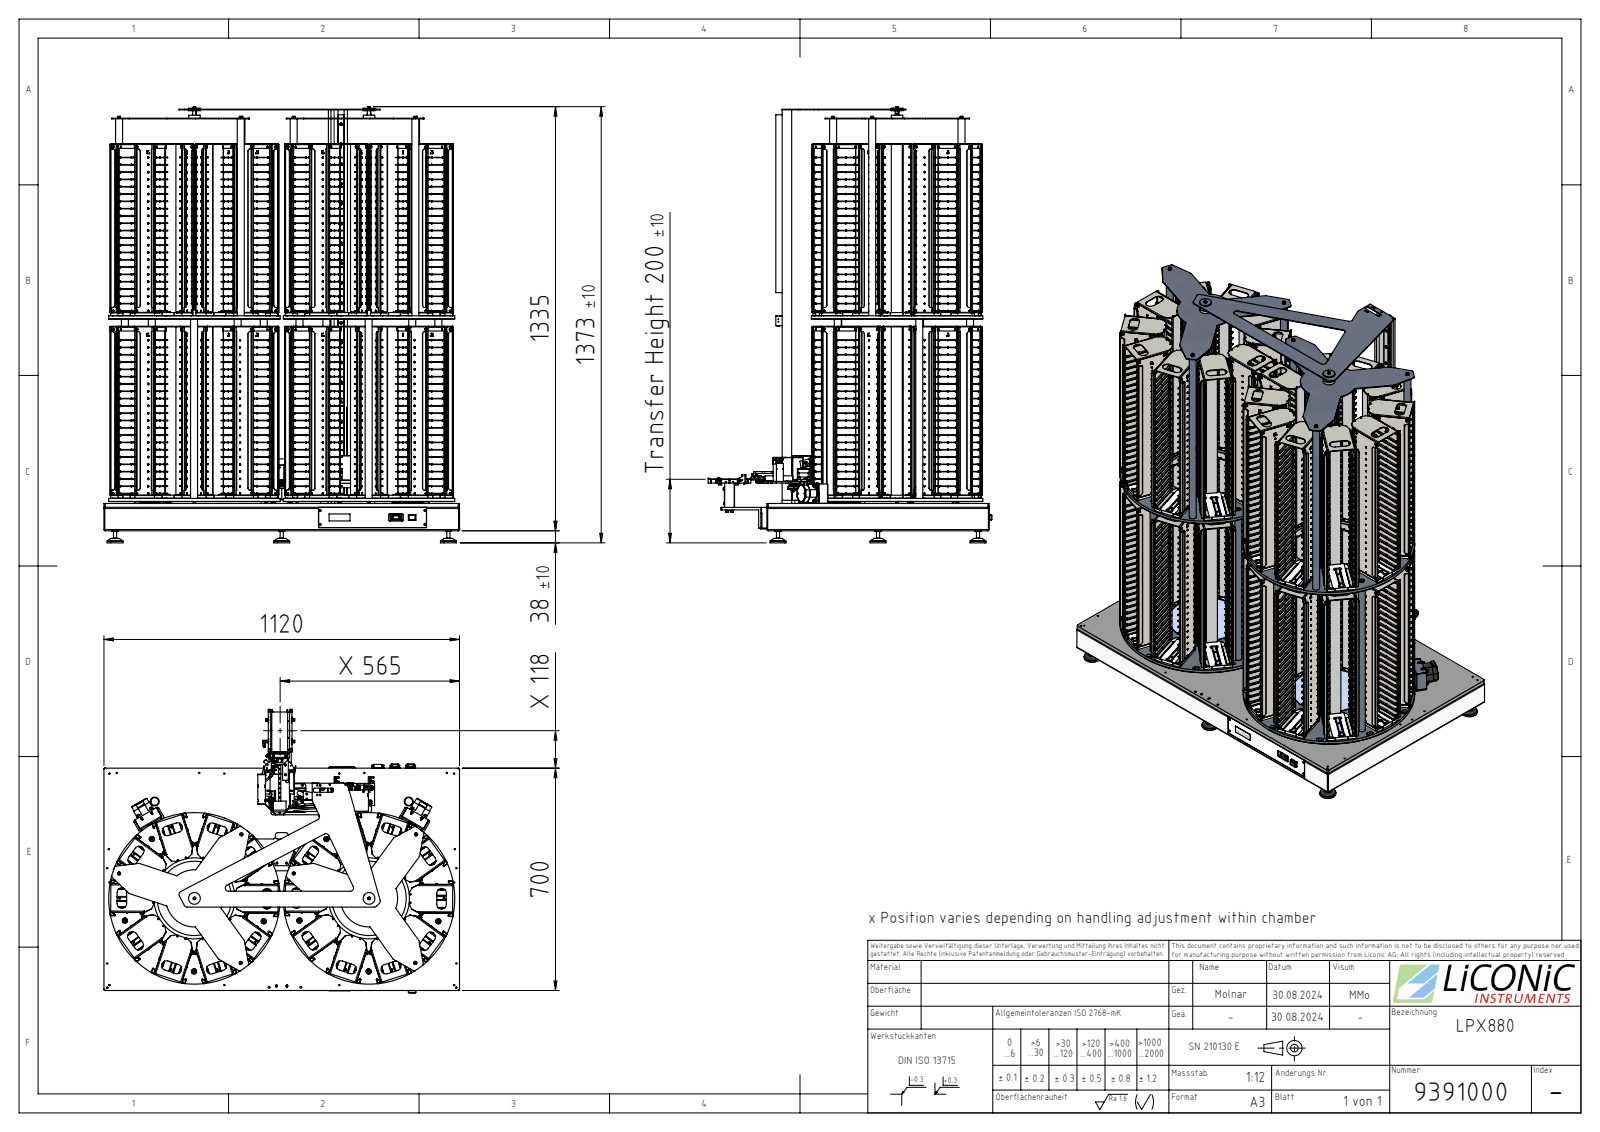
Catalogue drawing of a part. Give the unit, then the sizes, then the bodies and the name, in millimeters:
Units: millimetres
Overall size (bounding box): 1365.3 × 1120 × 893.98
Round holes (diameter × count): ⌀4 ×176, ⌀2.5 ×78, ⌀4.2 ×73, ⌀3.3 ×51, ⌀6.5 ×21, ⌀4.5 ×16, ⌀4.7 ×16, ⌀6 ×16, ⌀6.8 ×16, ⌀8.5 ×16, ⌀8 ×12, ⌀5.3 ×10
Round bosses / shafts (diameter × count): ⌀22 ×16, ⌀50.01 ×7, ⌀10 ×7, ⌀1.5 ×3, ⌀540 ×2, ⌀234 ×2, ⌀15.5 ×1, ⌀14.5 ×1
Partial cylindrical surfaces — rounded edges, fillets, slot ends (radius × count): R0.1 ×1660, R0.25 ×1656, R2 ×827, R2.5 ×156, R5 ×133, R1 ×87, R1.5 ×44, R7 ×44
Main face-to-face distances: 2, 72, 10, 74, 575, 12, 84, 86, 1, 16
Hole centre spacings: 23, 46, 69, 92, 115, 138, 161, 62.5
Volume: 26 200 000 mm³ · Surface area: 9 006 000 mm²
Bodies: 76 solids, 13941 faces (7320 planar, 6431 cylindrical, 190 other)
Part name (STEP PRODUCT): 9391000
STEP written by: SolidWorks 2022 (AUTOMOTIVE_DESIGN)
